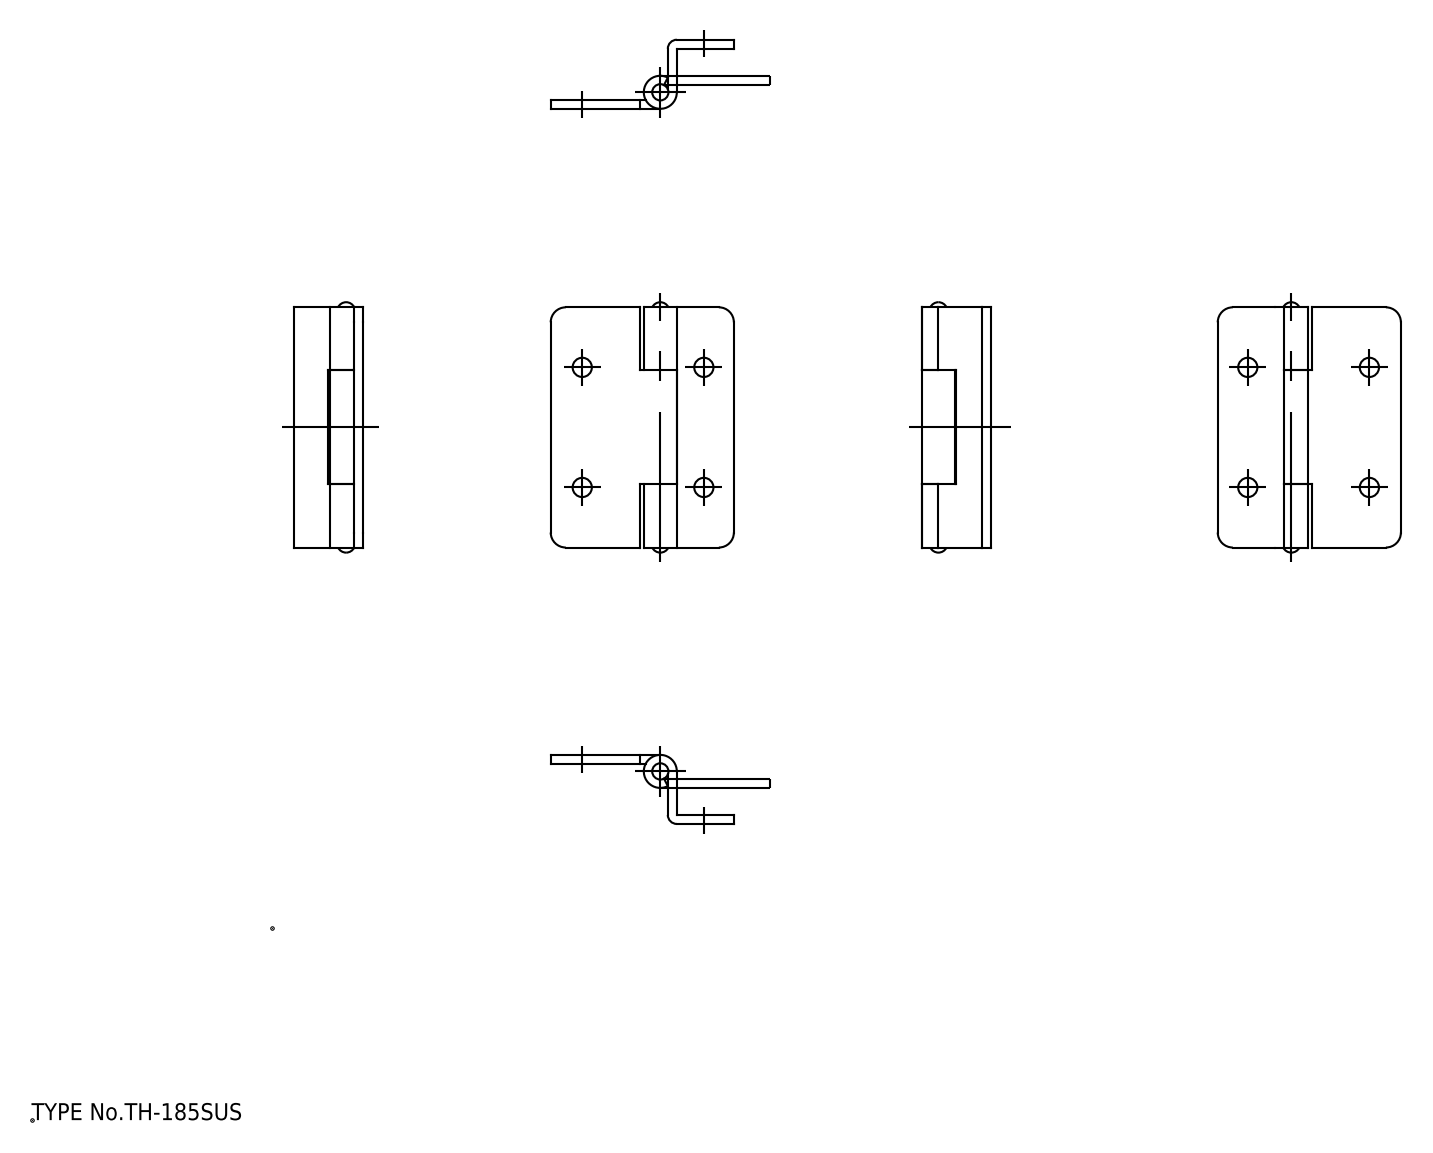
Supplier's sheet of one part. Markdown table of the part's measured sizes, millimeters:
| quantity | value |
| --- | --- |
| part name | シャフト; ヒンジA; ヒンジB |
| STEP written by | spGate 19.8.4 (****-****-****-****) (AUTOMOTIVE_DESIGN) |
| units | millimeters |
| bodies | 3 solids, 49 faces (24 planar, 21 cylindrical, 4 other) |
| overall size | 41.7 × 30.5 × 11.5 |
| volume | 2 743 mm³ |
| surface area | 4 224 mm² |
| round holes (diameter × count) | 3.2 × 4, 2.5 × 1 |
| round bosses / shafts (diameter × count) | 5.5 × 1 |
| partial cylindrical surfaces (radius × count) | 2.5 × 4, 1.5 × 1 |
| main face-to-face distances | 1.5, 10, 11.5, 8.5, 10.5, 29.5, 40, 11, 9.5, 19.5 |
| hole center spacings | 20, 20.25, 28.46 |
